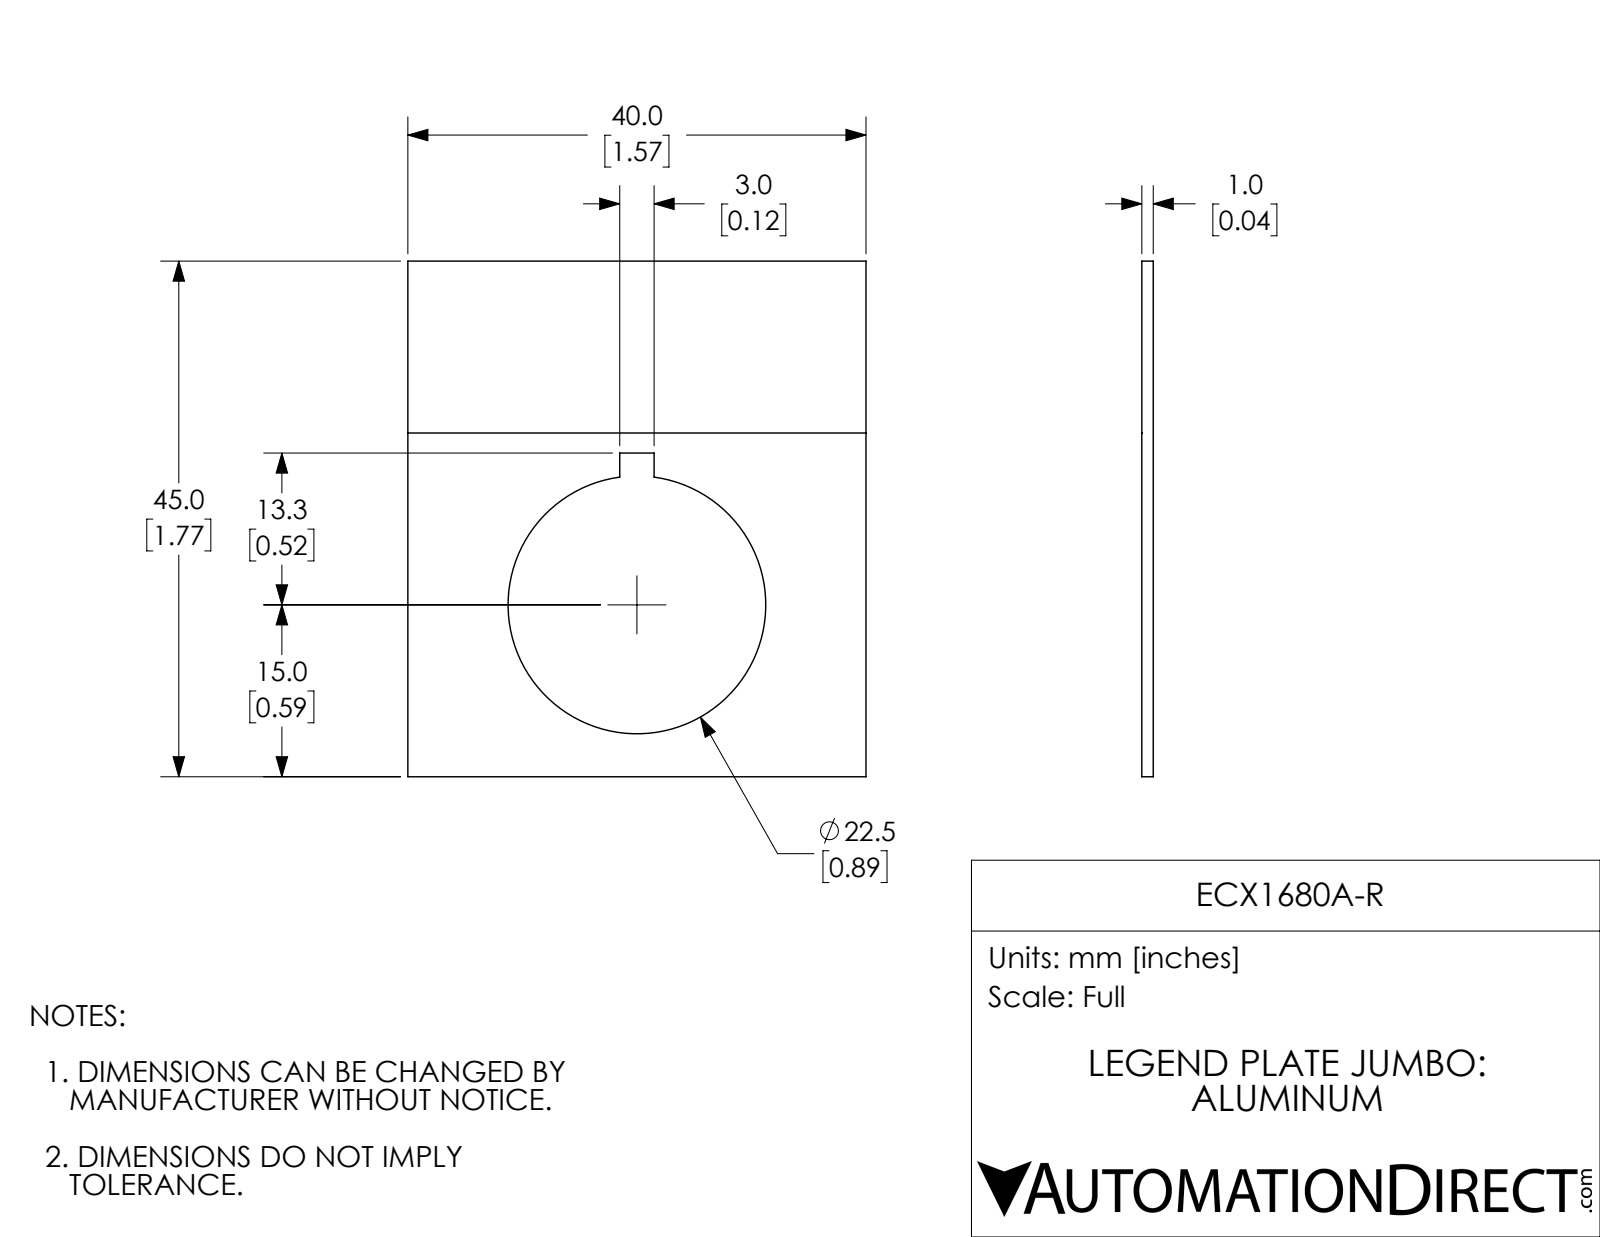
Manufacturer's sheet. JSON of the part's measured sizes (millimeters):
{"part_name": "ECX1680A-R", "step_written_by": "SolidWorks 2017 (AUTOMOTIVE_DESIGN)", "units": "millimeters", "bodies": {"solids": 1, "faces": 14, "planar": 11, "cylindrical": 3, "other": 0}, "overall_size": [45, 40, 1], "volume_mm3": 1393, "surface_area_mm2": 3037, "round_holes": [[22.5, 1]], "face_to_face_distances": [1, 0.99, 40, 45, 18.5, 21.5, 28.25, 16.75, 3, 30]}
